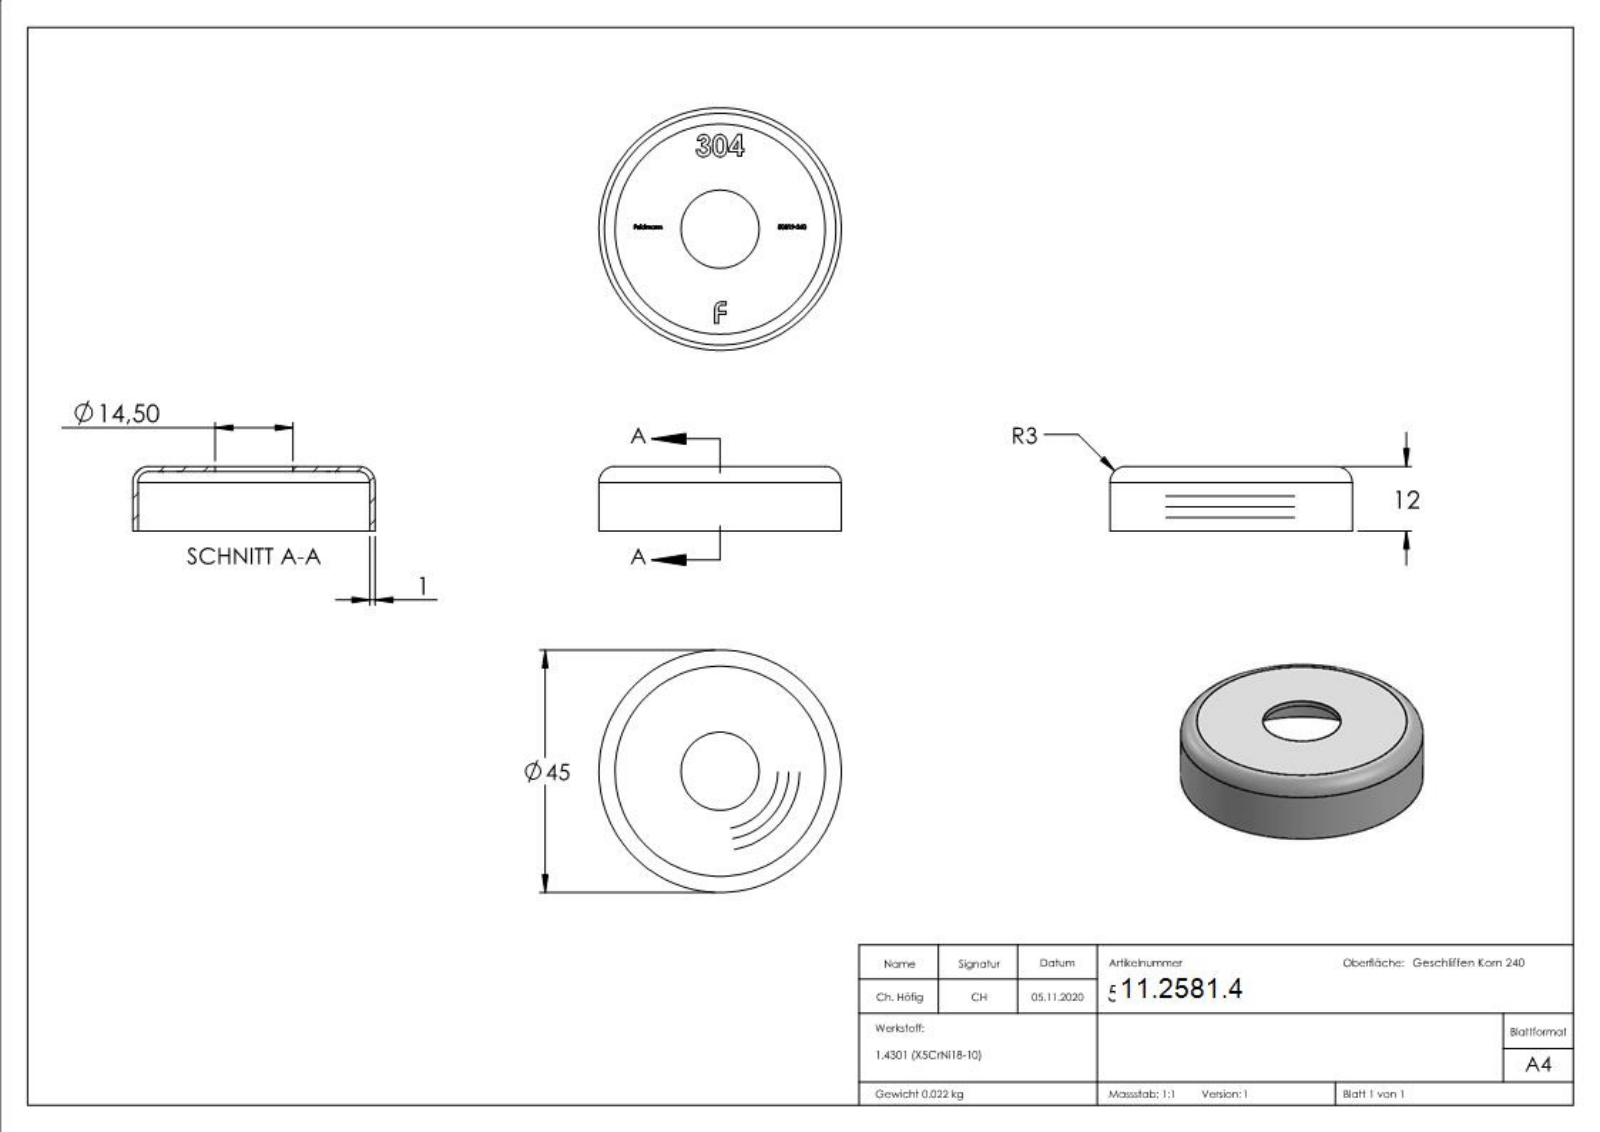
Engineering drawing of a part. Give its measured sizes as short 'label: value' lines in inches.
name: 50819-240
written by: SolidWorks 2018 (CONFIG_CONTROL_DESIGN)
unit: in
bodies: 1 solid, 295 faces (154 planar, 6 cylindrical, 135 other)
size: 1.772 × 1.772 × 0.472
volume: 0.17 in³; area: 8.97 in²
holes: 1× ⌀0.571, 1× ⌀1.693
bosses: 1× ⌀1.772
face distances: 0.039, 0.433, 0.472, 0.437, 0.035, 0.028, 0.197, 0.169, 0.023, 0.027
